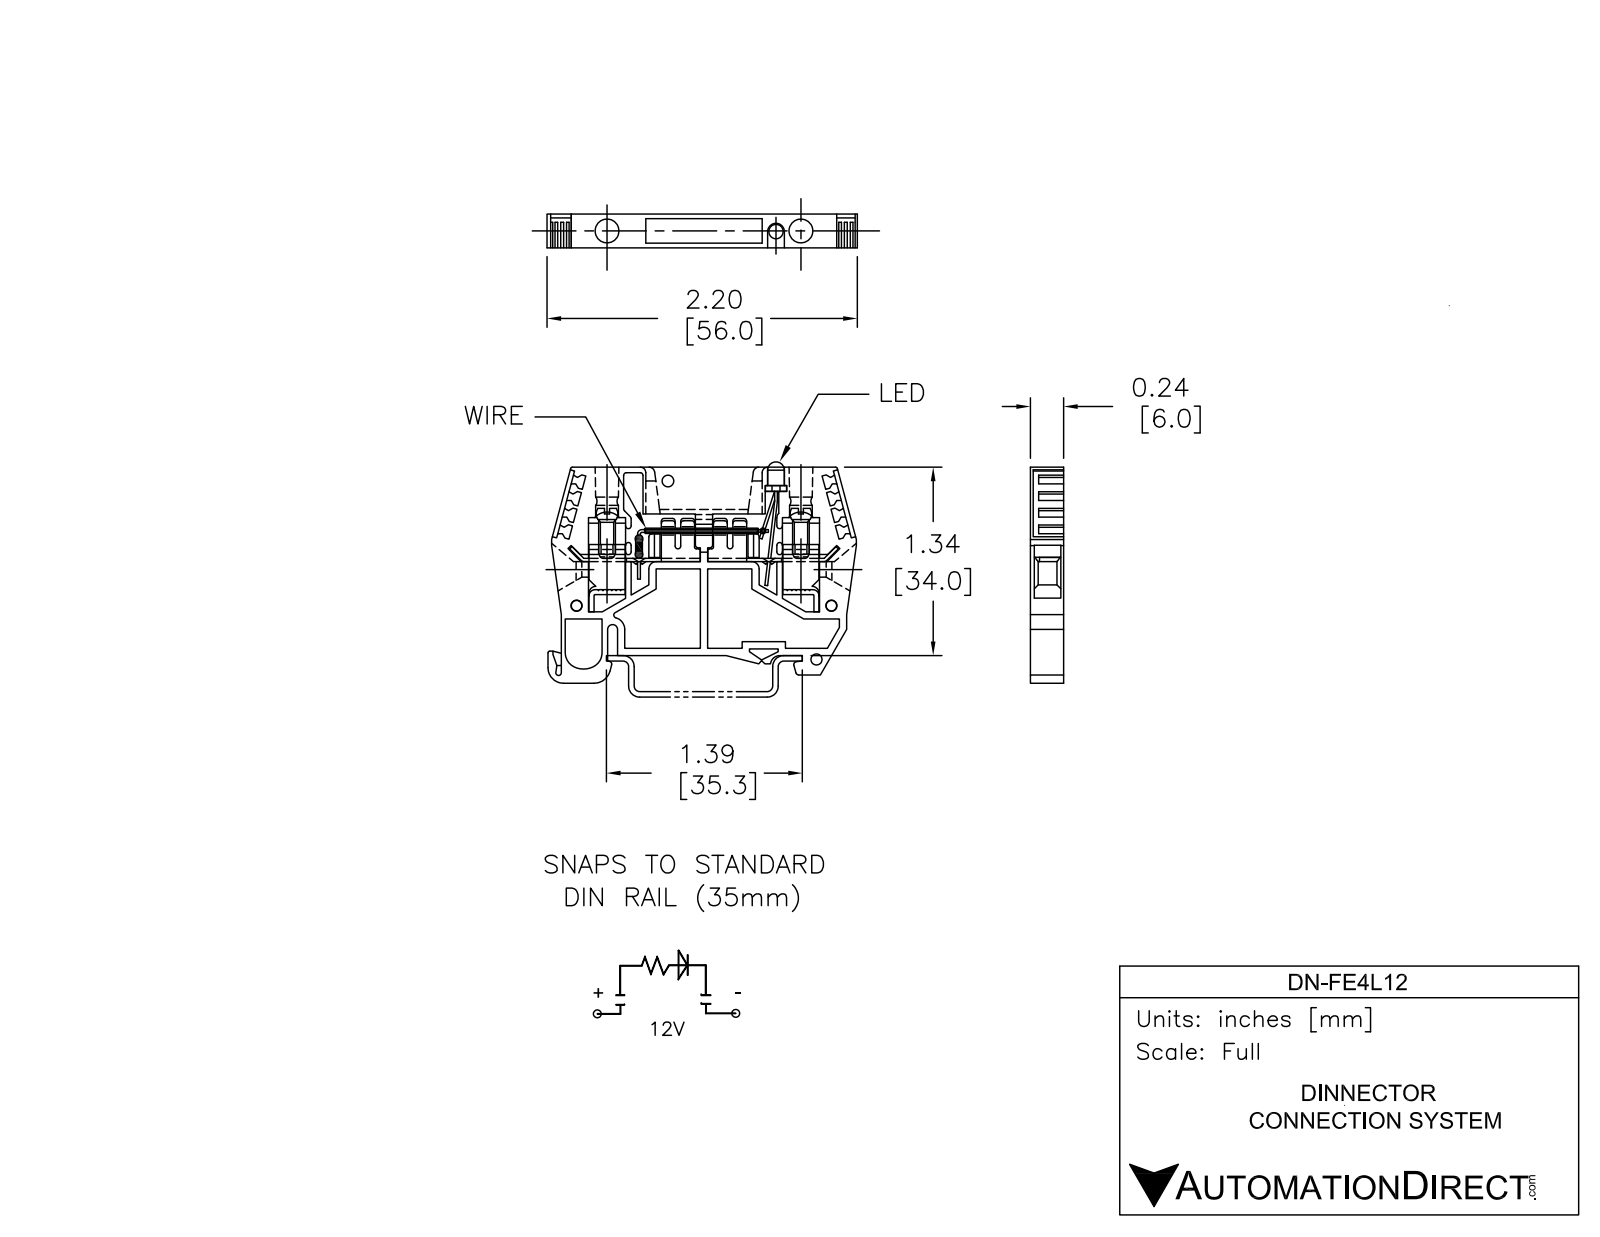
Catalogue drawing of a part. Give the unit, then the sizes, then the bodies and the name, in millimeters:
Units: millimetres
Overall size (bounding box): 55.65 × 39.6 × 6
Round holes (diameter × count): ⌀2 ×3, ⌀4.1 ×2
Round bosses / shafts (diameter × count): ⌀0.3 ×10, ⌀4 ×1, ⌀3 ×1
Partial cylindrical surfaces — rounded edges, fillets, slot ends (radius × count): R0.5 ×13, R3 ×5, R1 ×3, R1.3 ×2, R0.9 ×1, R1.05 ×1, R1.5 ×1, R1.7 ×1
Main face-to-face distances: 6, 0.5, 3.5, 2, 2.5, 5.5, 34, 2.2, 1.5, 3
Hole centre spacings: 10.07, 35, 44.38, 46
Volume: 9 020 mm³ · Surface area: 6 676 mm²
Bodies: 2 solids, 359 faces (227 planar, 91 cylindrical, 41 other)
Part name (STEP PRODUCT): 4358100_DN-QFE4; 20621_1; 4358101-DN-FE4L12
STEP written by: SolidWorks 2013 (AUTOMOTIVE_DESIGN)
